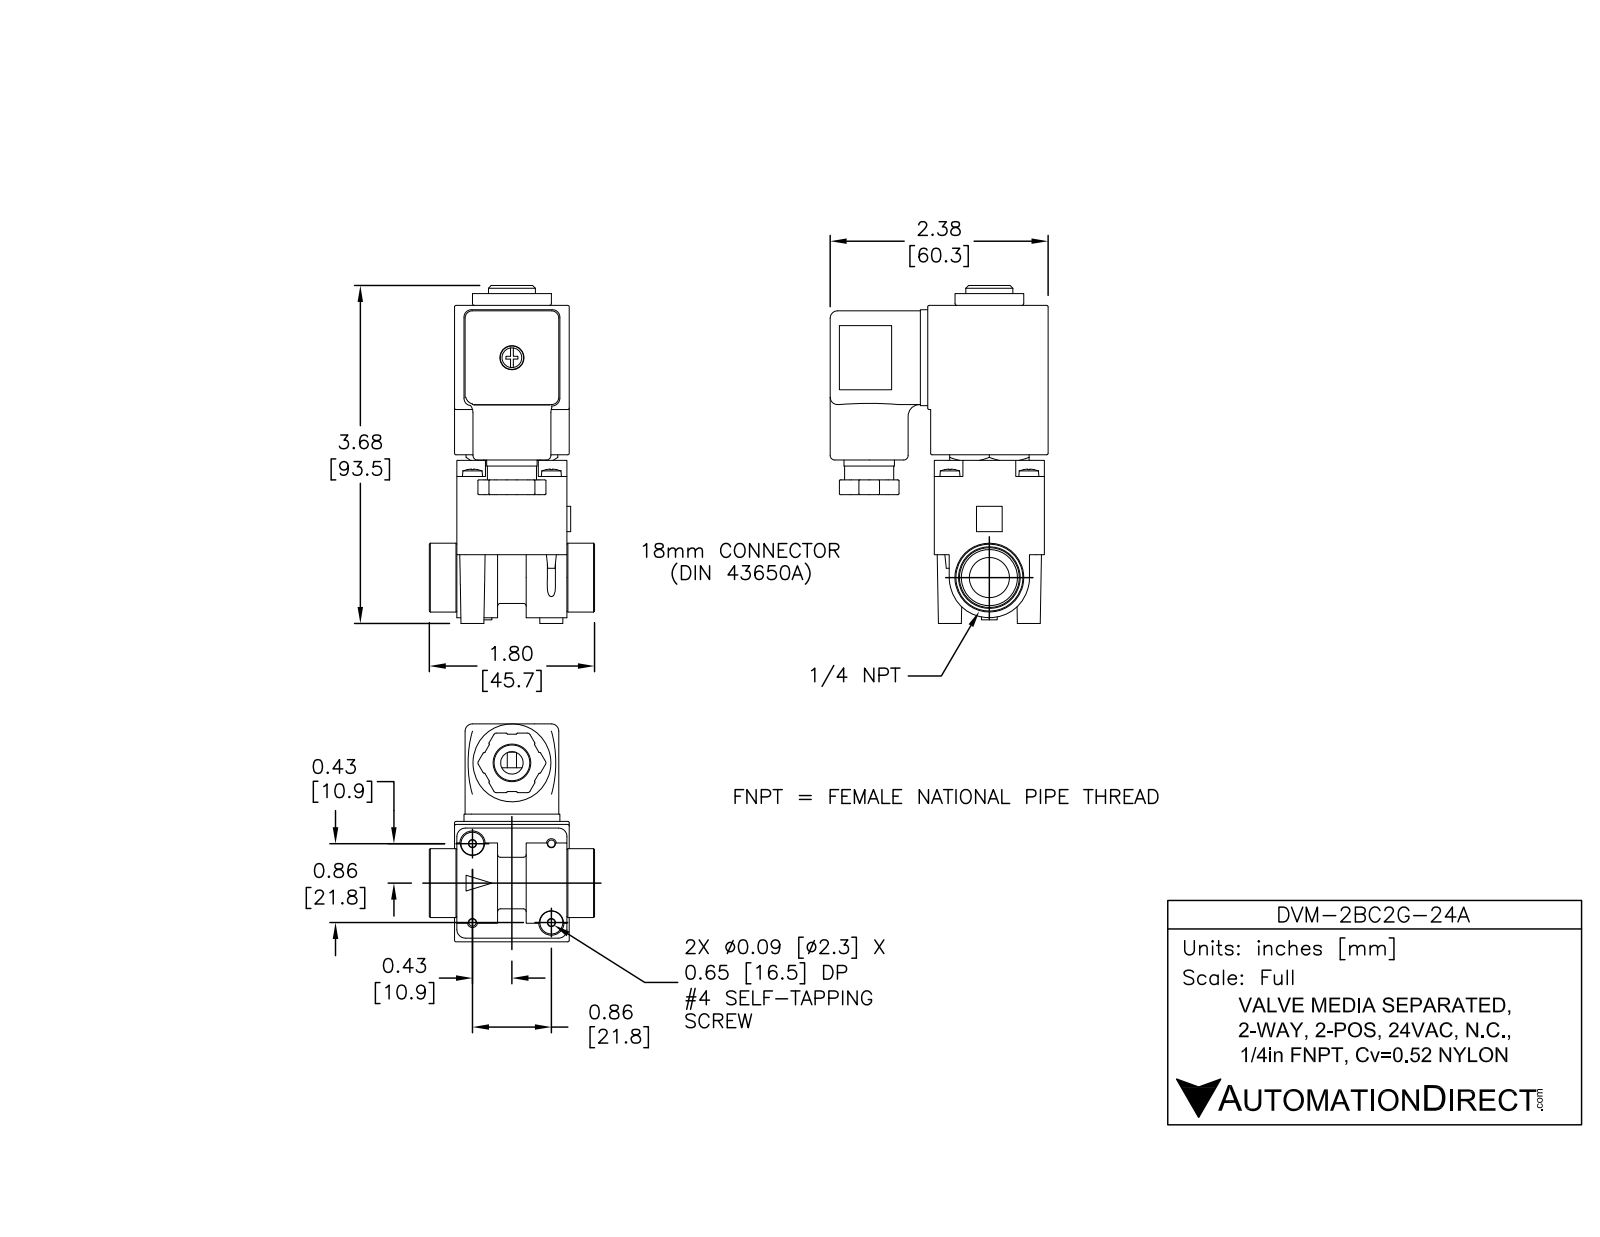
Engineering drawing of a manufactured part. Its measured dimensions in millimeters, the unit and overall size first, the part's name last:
Units: millimetres
Overall size (bounding box): 93.5 × 60.3 × 45.7
Round holes (diameter × count): ⌀2.8 ×4, ⌀1.5 ×2, ⌀2.3 ×2, ⌀8 ×2, ⌀3 ×1, ⌀4 ×1, ⌀5.2 ×1, ⌀6.2 ×1, ⌀6.4 ×1, ⌀6.7 ×1, ⌀9.9 ×1, ⌀10.2 ×1
Round bosses / shafts (diameter × count): ⌀5.5 ×4, ⌀3.2 ×4, ⌀21.6 ×1, ⌀20.5 ×1, ⌀19.1 ×1, ⌀17.3 ×1, ⌀13.6 ×1, ⌀13.2 ×1
Partial cylindrical surfaces — rounded edges, fillets, slot ends (radius × count): R0.3 ×54, R0.1 ×21, R0.4 ×17, R0.5 ×12, R0.8 ×12, R0.8 ×12, R2 ×12, R1.3 ×8
Main face-to-face distances: 31.8, 30.5, 4.1, 27.6, 1.2, 24.7, 0.6, 31.1, 0.6, 31.1
Hole centre spacings: 15.4, 15.4, 17.4, 21.8, 21.8, 24.9, 30.9, 37
Volume: 84 440 mm³ · Surface area: 43 410 mm²
Bodies: 14 solids, 1775 faces (895 planar, 351 cylindrical, 529 other)
Part name (STEP PRODUCT): DVM-2BC2G-24A
STEP written by: SolidWorks 2015 (AUTOMOTIVE_DESIGN)
